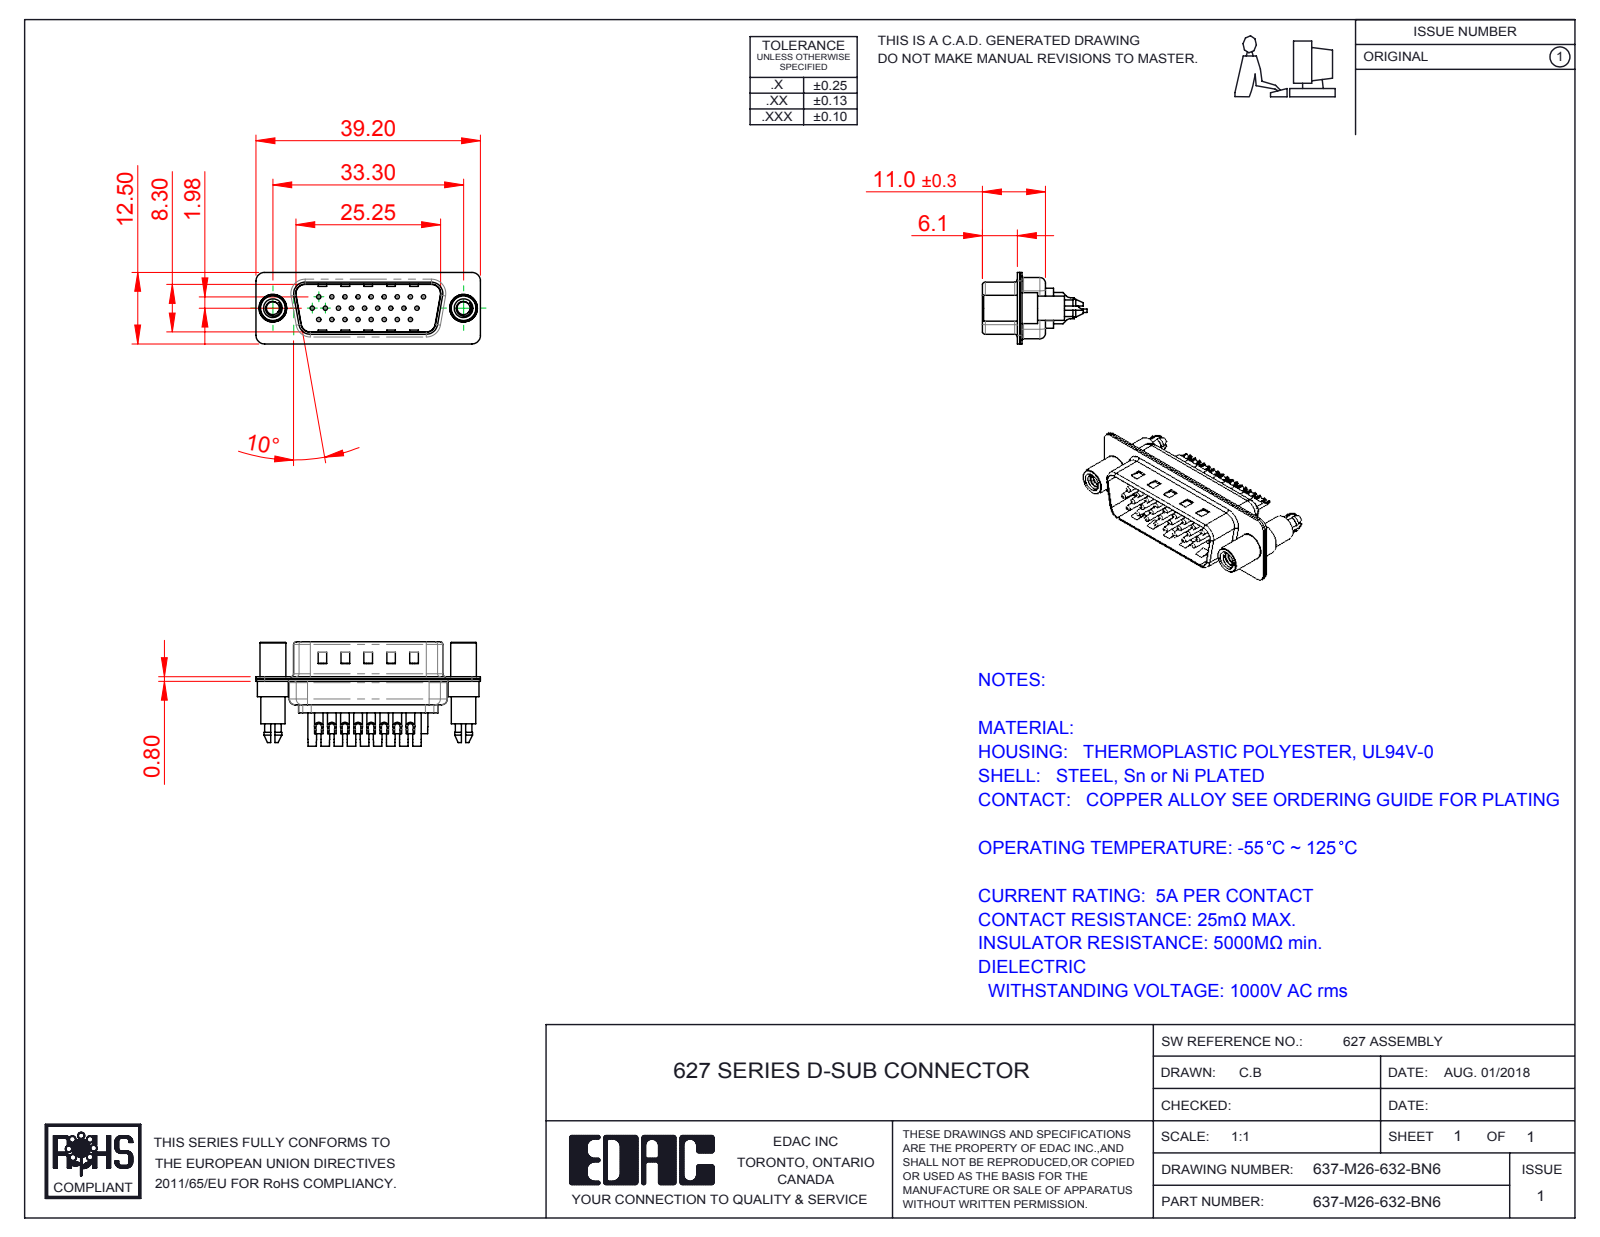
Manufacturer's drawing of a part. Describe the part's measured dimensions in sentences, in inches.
The part is named "637-M26-632-BN6; 637M 4-40 Threaded Standoff and Boardlock; 637M Housing_26 Contacts; 637M Contact Row 1_32 (+4 more)". Its 3-D file was written by "SolidWorks 2016 (CONFIG_CONTROL_DESIGN)". It is 31 solids with 1386 faces: 411 planar, 585 cylindrical and 390 other. Overall it measures 1.543 by 0.719 by 0.492 inches. Its volume is 0.142 cubic inches and its surface area 10.16 square inches. Round holes: 26 of diameter 0.03, 26 of diameter 0.039, 26 of diameter 0.063, 26 of diameter 0.079, 2 of diameter 0.089, 2 of diameter 0.157, 2 of diameter 0.189. Round bosses or shafts: 26 of diameter 0.059, 2 of diameter 0.213, 2 of diameter 0.193, 2 of diameter 0.177, 2 of diameter 0.167. Partial cylindrical surfaces (rounded edges, fillets, slot ends): 18 of radius 0.059, 12 of radius 0.079, 10 of radius 0.063, 8 of radius 0.02, 7 of radius 0.039, 4 of radius 0.01, 4 of radius 0.024, 4 of radius 0.026. The main face-to-face distances are 0.016, 0.031, 0.374, 0.358, 0.343, 0.39, 0.03, 0.014, 0.047, 0.075. The hole center spacings are 0.156, 0.09, 0.18, 0.238, 0.09, 0.324, 0.27, 0.413.
